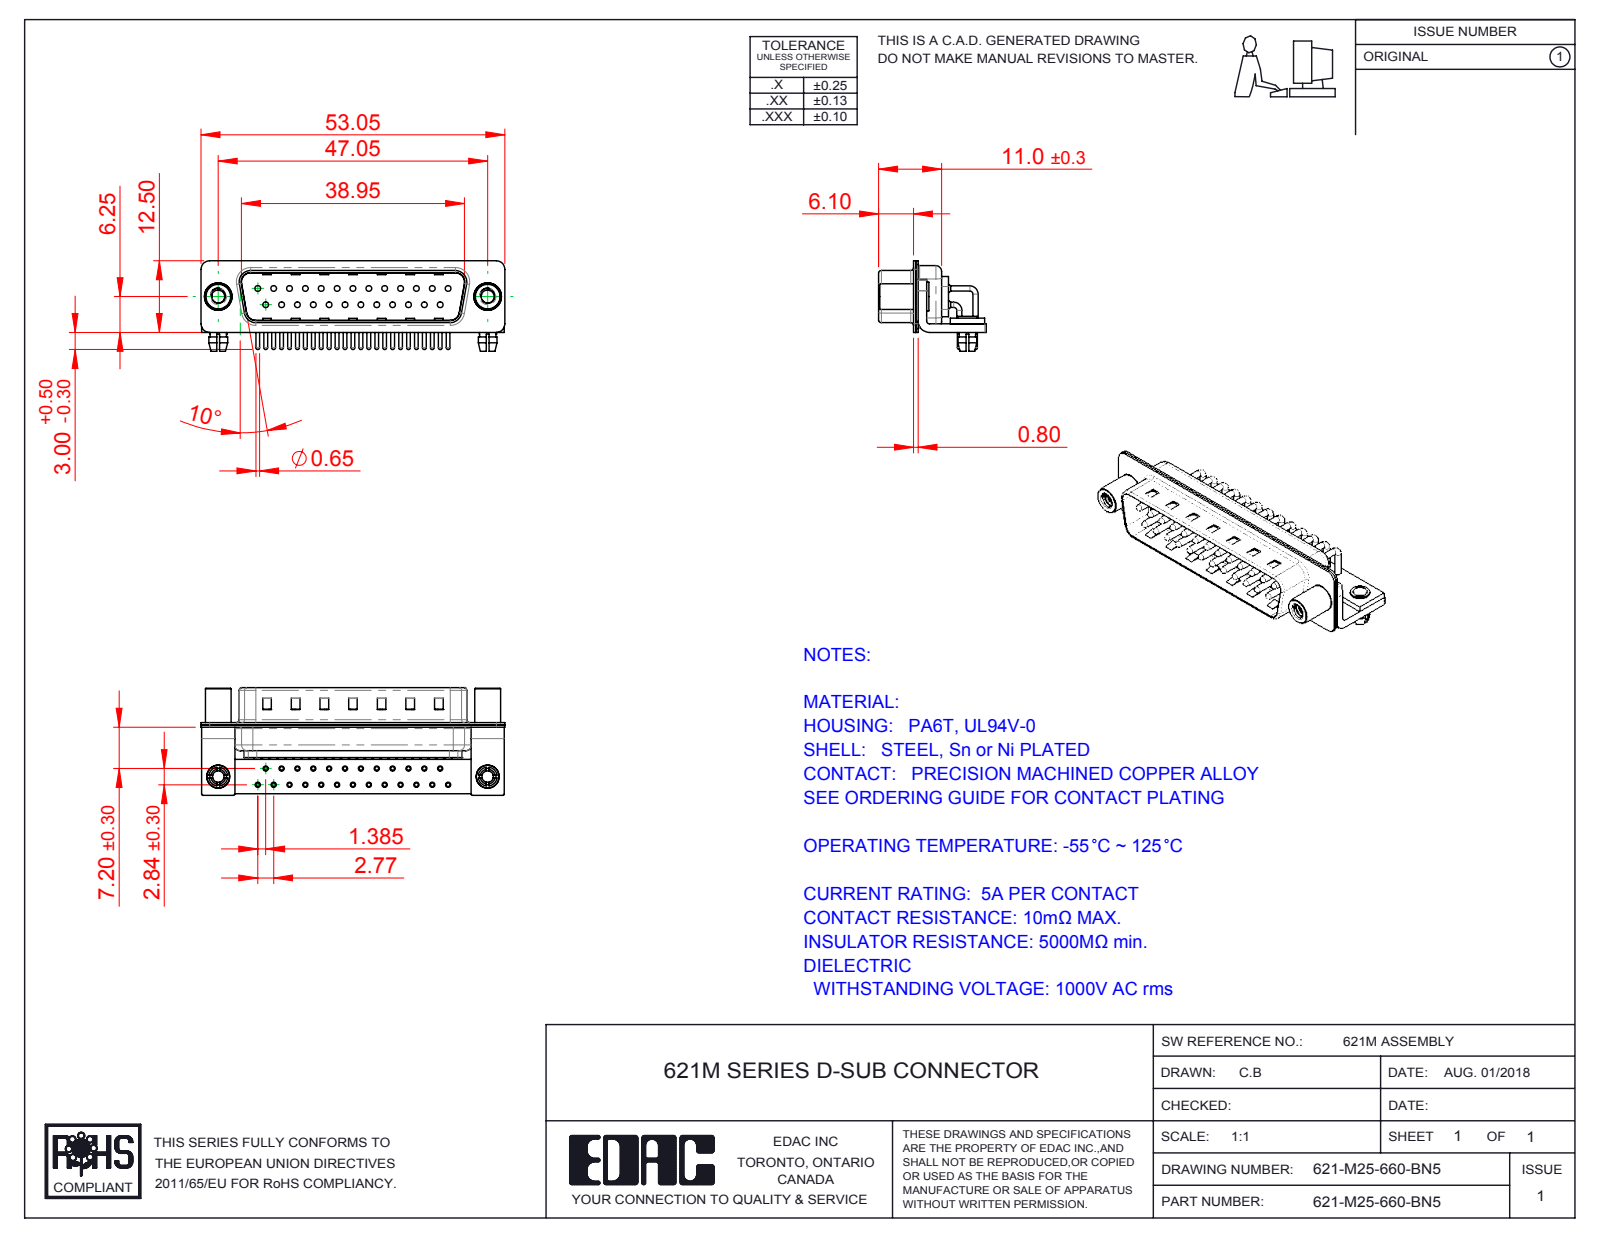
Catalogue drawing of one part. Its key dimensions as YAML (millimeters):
part_name: "621M 4-40 Threaded Standoff; 621M Stabilizer Board_25 Contacts; 621M Stabilizer Bracket; 621M Shell Rear_25 Contacts (+6 more)"
step_written_by: "SolidWorks 2016 (CONFIG_CONTROL_DESIGN)"
units: millimeters
bodies: {solids: 35, faces: 3368, planar: 1847, cylindrical: 1183, other: 338}
overall_size: [53.05, 18.8, 15.8]
volume: 3558
surface_area: 9450
round_holes:
  - {diameter: 2, count: 27}
  - {diameter: 0.9, count: 25}
  - {diameter: 1, count: 25}
  - {diameter: 1.7, count: 25}
  - {diameter: 2.26, count: 2}
  - {diameter: 2.5, count: 2}
  - {diameter: 3.2, count: 2}
  - {diameter: 4, count: 2}
  - {diameter: 4.8, count: 2}
round_bosses_or_shafts:
  - {diameter: 0.9, count: 33}
  - {diameter: 1.5, count: 25}
  - {diameter: 0.65, count: 25}
  - {diameter: 5, count: 2}
  - {diameter: 4.9, count: 2}
  - {diameter: 4.5, count: 2}
  - {diameter: 4, count: 2}
  - {diameter: 3.4, count: 2}
partial_cylinders:
  - {radius: 1.01, count: 25}
  - {radius: 0.25, count: 16}
  - {radius: 1.5, count: 16}
  - {radius: 2, count: 13}
  - {radius: 0.5, count: 9}
  - {radius: 1.6, count: 8}
  - {radius: 0.6, count: 4}
  - {radius: 0.65, count: 4}
face_to_face_distances: [0.4, 0.85, 1.25, 1.5, 9.55, 0.8, 10.4, 8.3, 1, 1.9]
hole_center_spacings: [3.16, 2.77, 8.31, 5.54, 11.08, 13.85, 5.04, 16.62]
